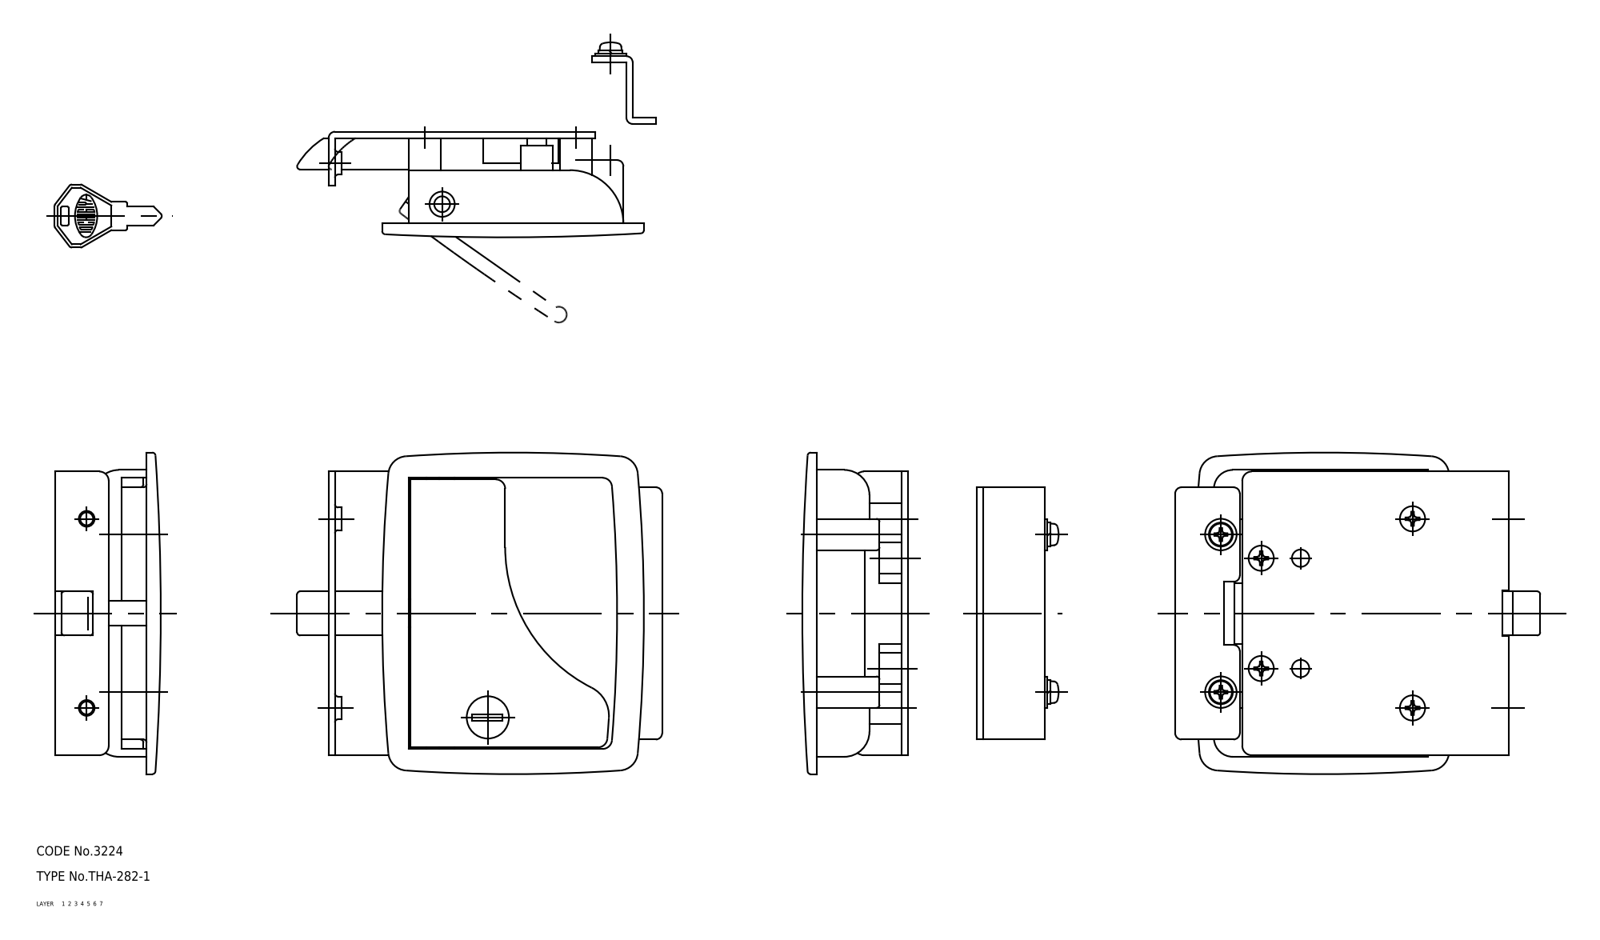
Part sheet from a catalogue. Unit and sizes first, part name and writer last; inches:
Units: inches
Overall size (bounding box): 4.508 × 4.016 × 3.761
Volume: 5.786 in³ · Surface area: 115.6 in²
Bodies: 9 solids, 583 faces (0 planar, 0 cylindrical, 583 other)
Part name (STEP PRODUCT): bracket_B; screw; lock; latch (+5 more)
STEP written by: CADfix (AUTOMOTIVE_DESIGN)
